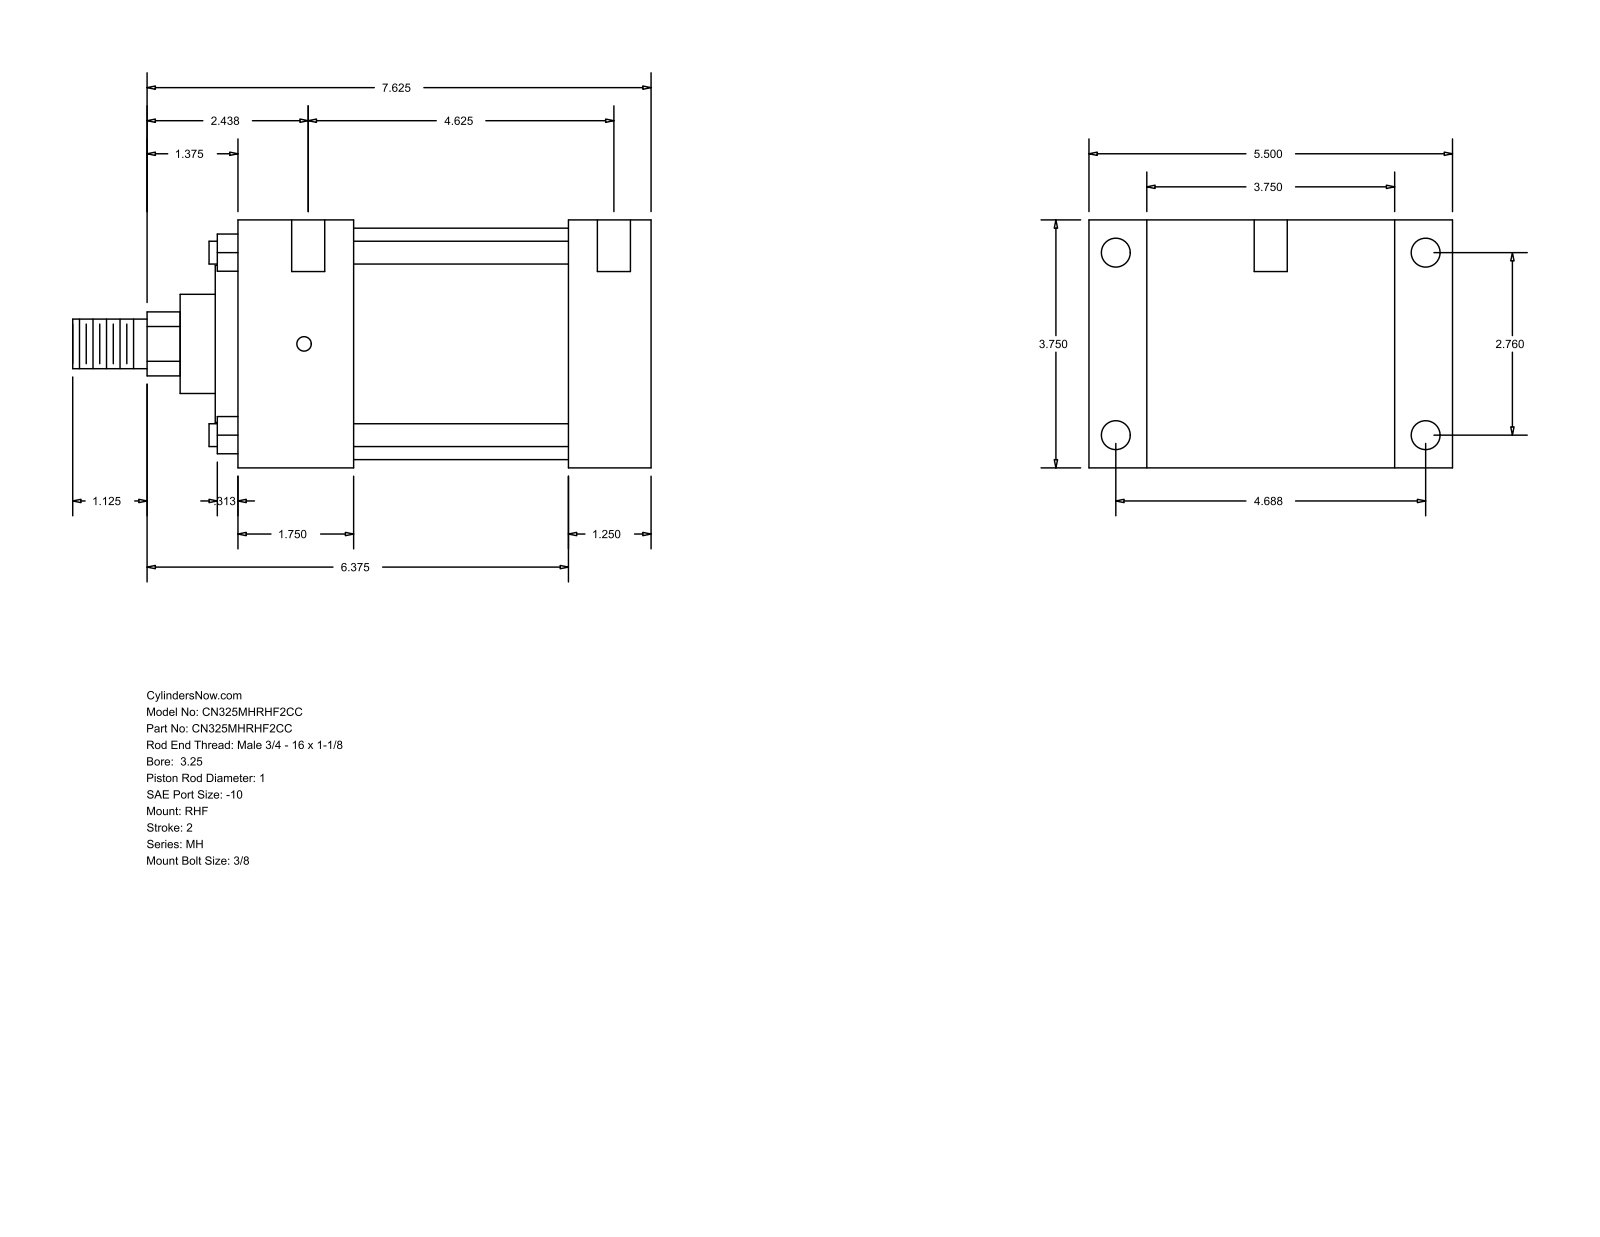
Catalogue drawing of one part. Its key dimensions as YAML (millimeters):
part_name: "MH_RHF__0325_1"
step_written_by: "GSSL Pune (CONFIG_CONTROL_DESIGN)"
units: millimeters
bodies: {solids: 0, faces: 90, planar: 61, cylindrical: 29, other: 0}
overall_size: [222.25, 139.7, 95.25]
round_holes:
  - {diameter: 5.56, count: 4}
  - {diameter: 11.13, count: 4}
  - {diameter: 12.7, count: 2}
round_bosses_or_shafts:
  - {diameter: 8.76, count: 4}
  - {diameter: 88.9, count: 1}
  - {diameter: 60.33, count: 1}
  - {diameter: 38.1, count: 1}
  - {diameter: 25.4, count: 1}
  - {diameter: 19.05, count: 1}
partial_cylinders:
  - {radius: 12.29, count: 1}
face_to_face_distances: [95.24, 31.75, 22.23, 117.47, 127.01, 158.76, 139.7, 44.46, 82.55, 114.3]
hole_center_spacings: [119.06, 70.1, 123.82, 138.16, 1.58, 4.76, 117.48, 122.24]
